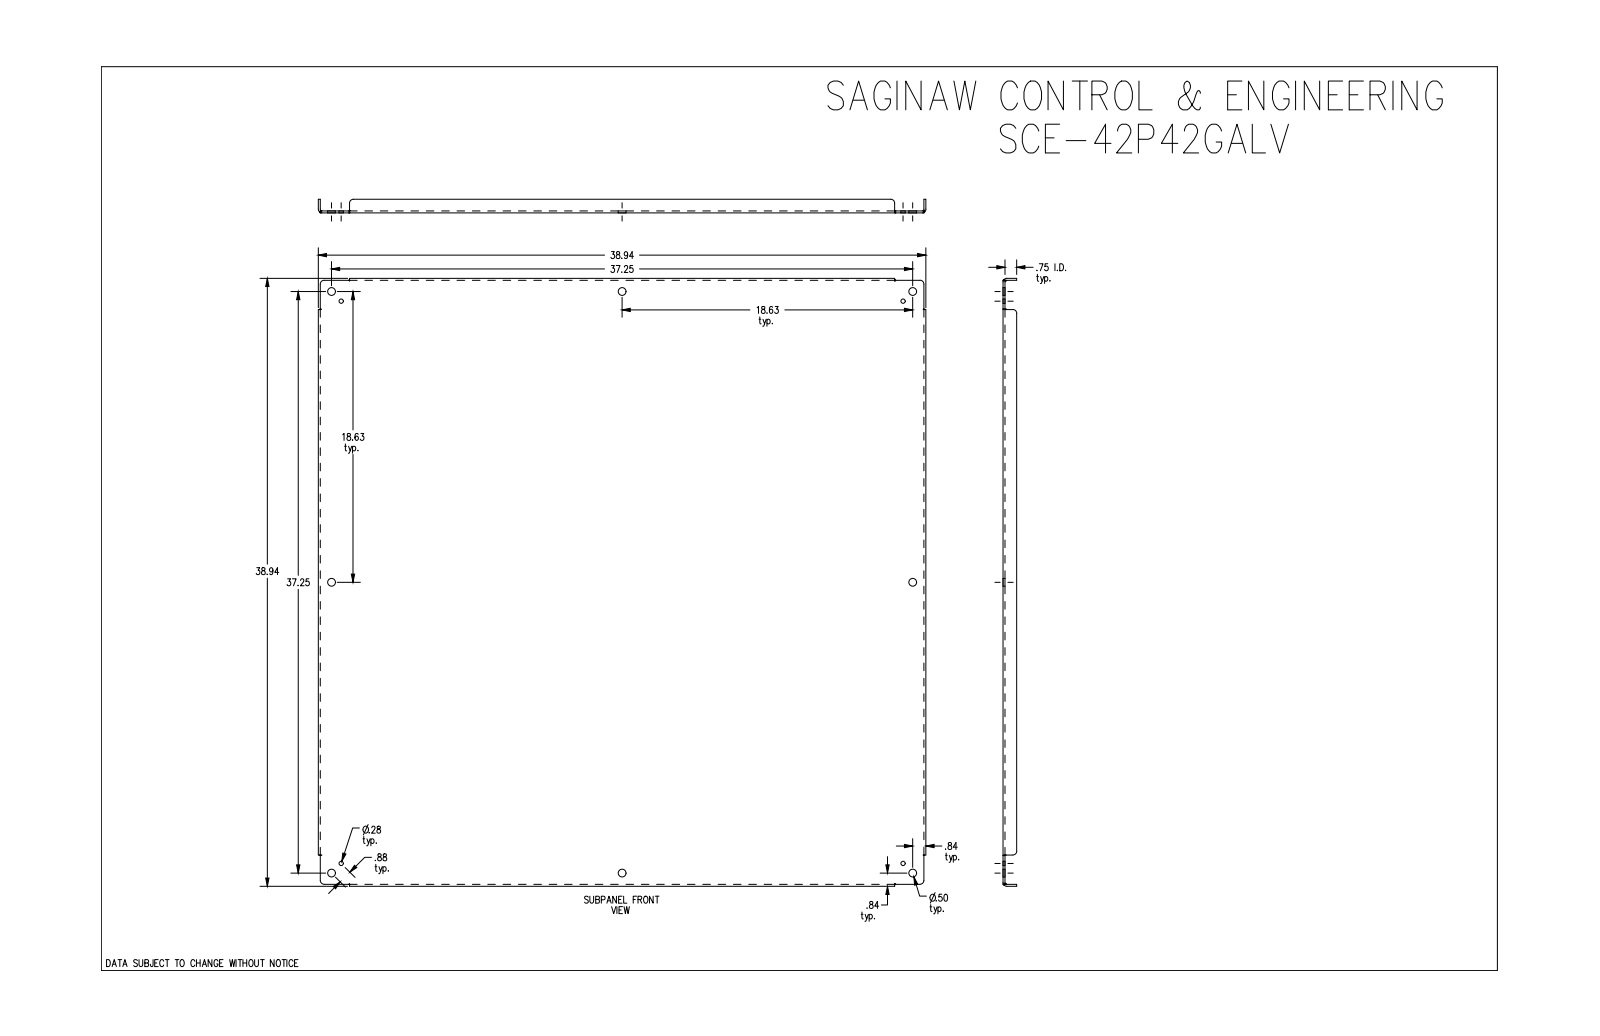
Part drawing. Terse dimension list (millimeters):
name: SCE-42P42GALV
written by: SolidWorks 2019 (CONFIG_CONTROL_DESIGN)
unit: mm
bodies: 1 solid, 86 faces (30 planar, 32 cylindrical, 24 other)
size: 989 × 989 × 22.2
volume: 3 291 000 mm³; area: 2 087 000 mm²
holes: 8× ⌀12.7, 4× ⌀7.1
rounds: 8× R6.4, 4× R2.8, 4× R6
face distances: 3.2, 3.2, 985.9, 982.6, 989, 19.1, 22.2, 50.8, 938.2, 47.6
hole spacings: 457.6, 473.1, 930.6, 1036.8, 1057.8, 946.2, 22.2, 669
